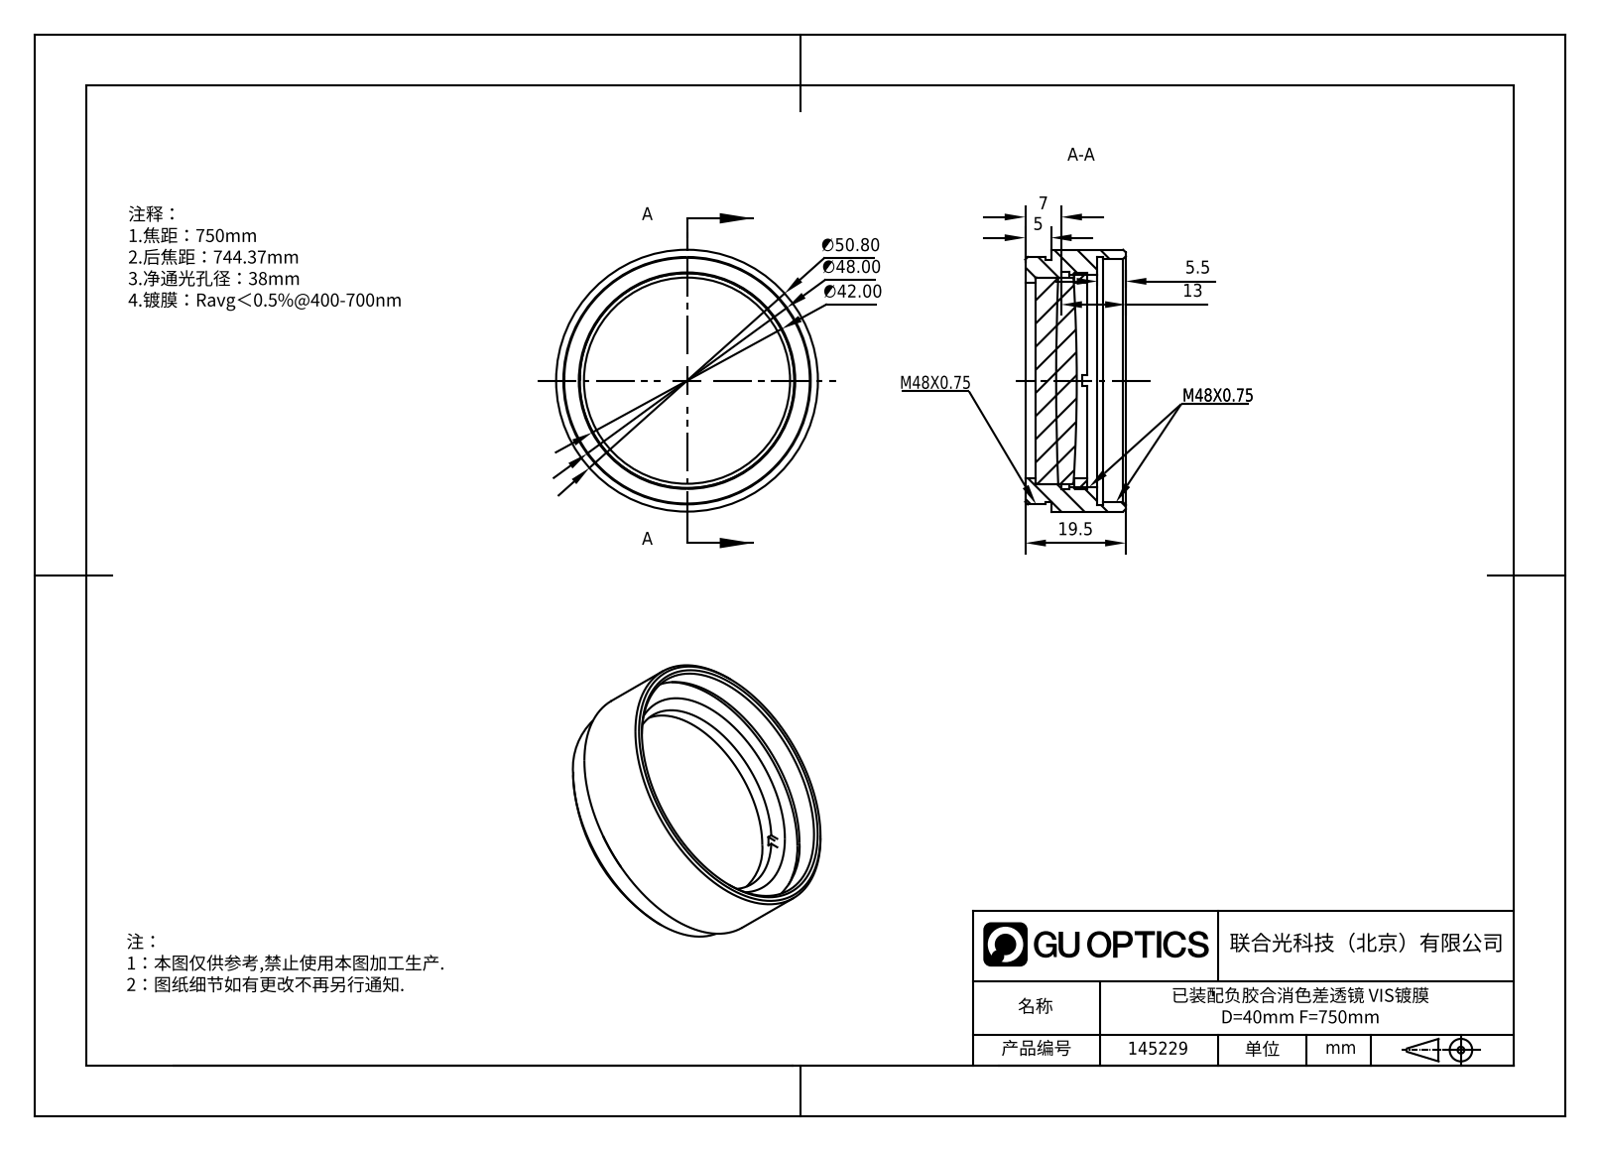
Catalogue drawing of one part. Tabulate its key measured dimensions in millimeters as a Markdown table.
| quantity | value |
| --- | --- |
| part name | M42x0.75ѹȦ; M42x0.75安装环PN35008-LM400-D1; APD-ML40-750-VIS-A; GL31-040-750-VIS_Solidworks |
| STEP written by | SolidWorks 2022 (AUTOMOTIVE_DESIGN) |
| units | millimeters |
| bodies | 4 solids, 64 faces (18 planar, 26 cylindrical, 20 other) |
| overall size | 50.8 × 50.8 × 19.5 |
| volume | 20 872 mm³ |
| surface area | 14 742 mm² |
| round holes (diameter × count) | 38 × 1, 41.25 × 1, 42.1 × 1, 47.25 × 1, 48.1 × 1 |
| round bosses / shafts (diameter × count) | 50.8 × 1, 48 × 1, 47 × 1, 42 × 1, 40 × 1 |
| main face-to-face distances | 14, 5, 2, 9, 7, 11.92, 6.92, 2.08, 9.42, 4.42 |
